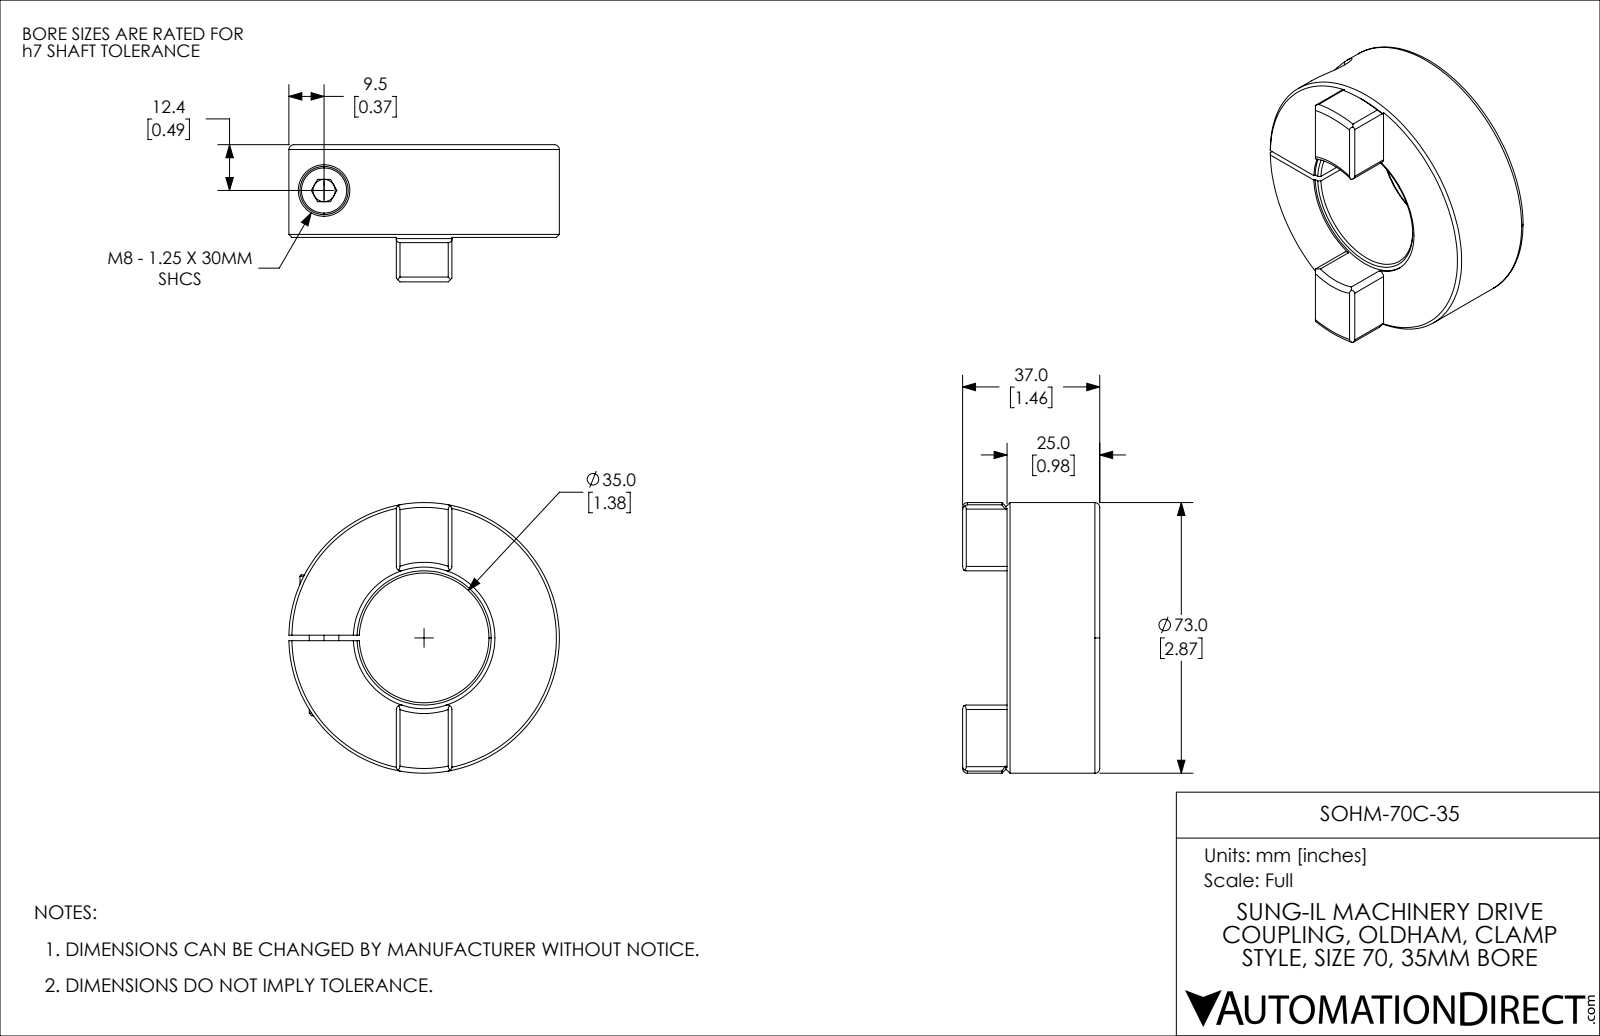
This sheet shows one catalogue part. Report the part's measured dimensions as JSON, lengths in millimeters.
{"part_name": "SOHM-70C-35", "step_written_by": "SolidWorks 2021 (CONFIG_CONTROL_DESIGN)", "units": "millimeters", "bodies": {"solids": 2, "faces": 90, "planar": 35, "cylindrical": 30, "other": 25}, "overall_size": [73, 72.99, 37], "volume_mm3": 84569, "surface_area_mm2": 19428, "round_holes": [[6, 1], [6.8, 1], [8.5, 1], [13.9, 1], [35, 1], [38.2, 1]], "round_bosses_or_shafts": [[73, 1], [13, 1], [8, 1]], "partial_cylinders_radius": [[1.2, 8], [50, 1]], "face_to_face_distances": [25, 1.5, 37, 12, 15, 9.75, 8.25, 24.5, 0.5, 12.5]}
